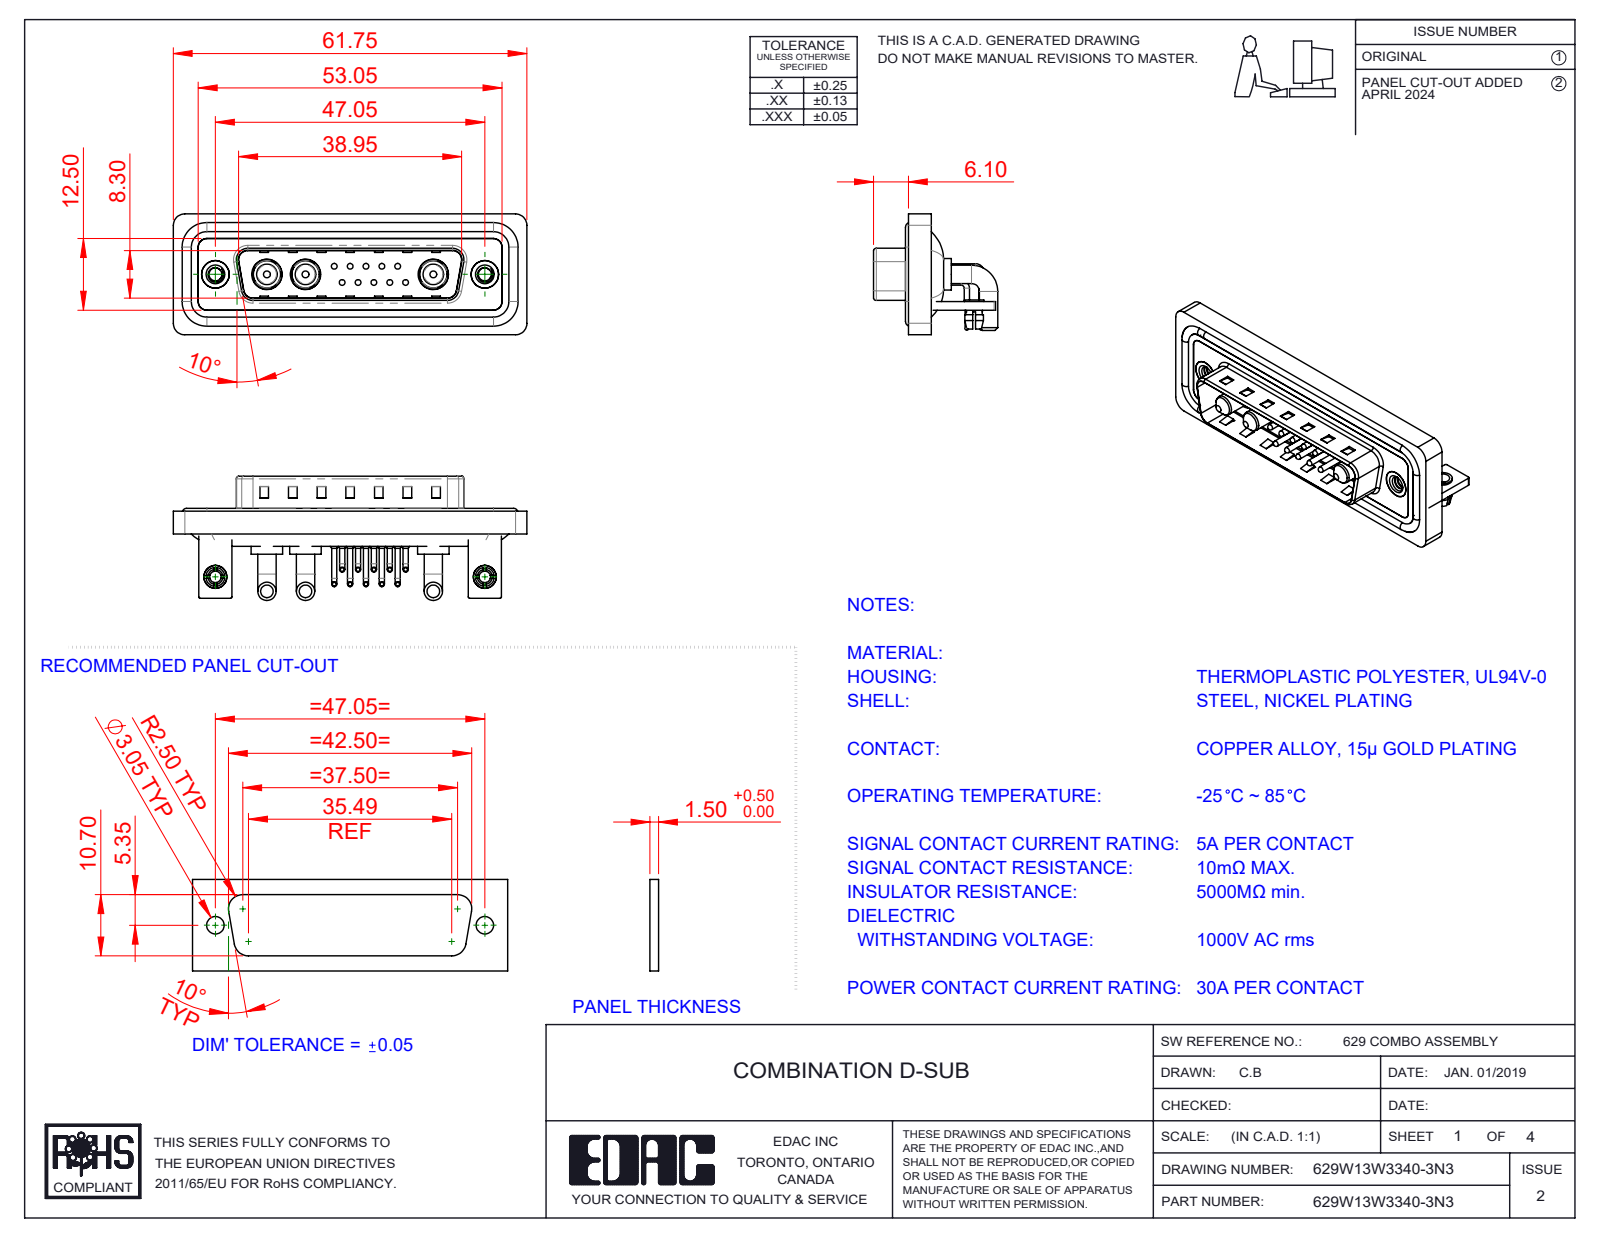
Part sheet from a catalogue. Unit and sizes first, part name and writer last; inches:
Units: inches
Overall size (bounding box): 2.431 × 0.854 × 0.831
Round holes (diameter × count): ⌀0.079 ×12, ⌀0.03 ×10, ⌀0.063 ×10, ⌀0.191 ×3, ⌀0.209 ×3, ⌀0.089 ×2, ⌀0.098 ×2, ⌀0.126 ×2, ⌀0.157 ×2, ⌀0.189 ×2, ⌀0.197 ×2
Round bosses / shafts (diameter × count): ⌀0.035 ×20, ⌀0.059 ×10, ⌀0.039 ×10, ⌀0.026 ×10, ⌀0.126 ×6, ⌀0.063 ×4, ⌀0.217 ×3, ⌀0.205 ×3
Partial cylindrical surfaces — rounded edges, fillets, slot ends (radius × count): R0.079 ×19, R0.059 ×18, R0.01 ×16, R0.04 ×10, R0.02 ×9, R0.063 ×8, R0.024 ×4, R0.026 ×4
Main face-to-face distances: 0.016, 0.031, 0.059, 0.114, 0.083, 0.043, 0.161, 0.063, 0.146, 0.177
Hole centre spacings: 0.124, 0.109, 0.198, 0.218, 0.295, 0.198, 0.327, 0.398
Volume: 0.489 in³ · Surface area: 20.69 in²
Bodies: 27 solids, 1844 faces (947 planar, 661 cylindrical, 236 other)
Part name (STEP PRODUCT): 629Combo Shell Rear_25 Contacts; 629Combo Contact Row 2; 629Combo Threaded Rivet_3; 629Combo Stabilizer Bracket (+7 more)
STEP written by: SolidWorks 2023 (CONFIG_CONTROL_DESIGN)
